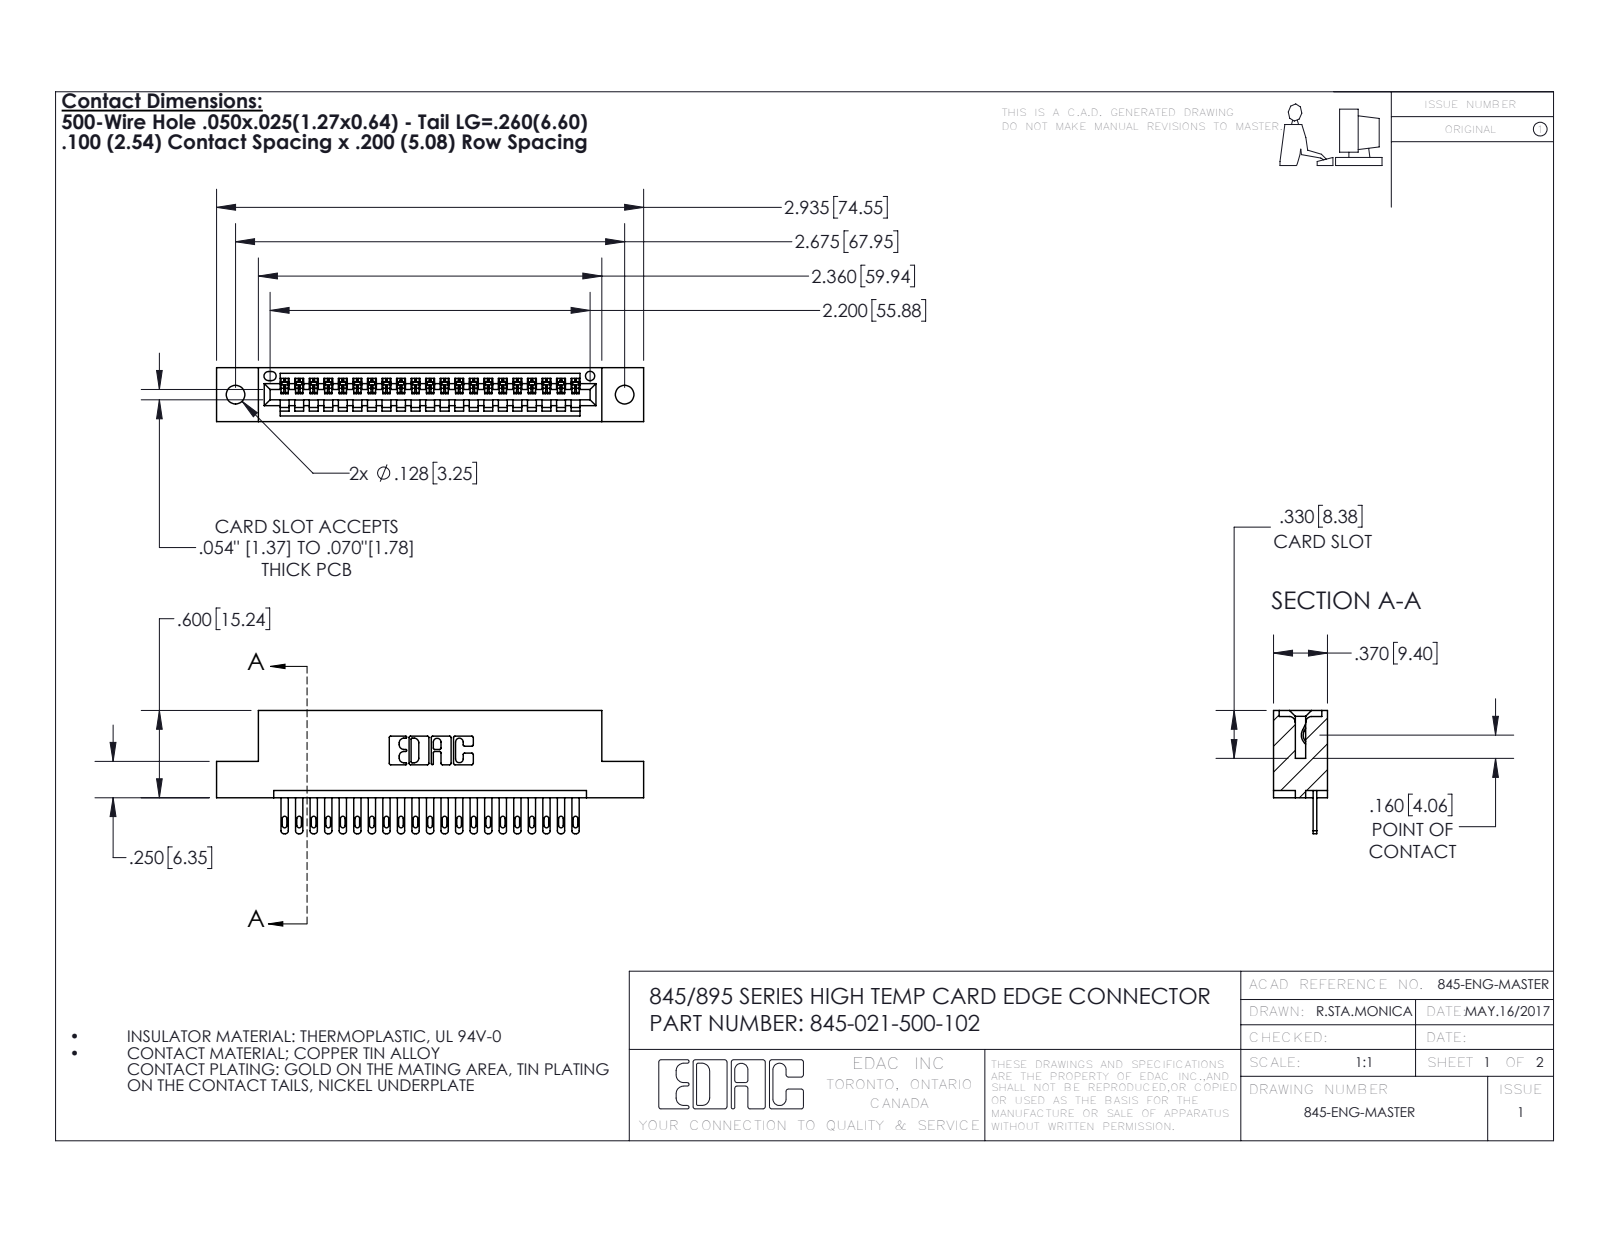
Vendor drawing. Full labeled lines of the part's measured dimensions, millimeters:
Part name (STEP PRODUCT): 345-292-001_345-293-100; 345 Part_Flush Mounting Lugs - 0.128 Dia; 345-021-500-102
STEP written by: SolidWorks 2016 (CONFIG_CONTROL_DESIGN)
Units: millimetres
Bodies: 22 solids, 1260 faces (794 planar, 466 cylindrical, 0 other)
Overall size (bounding box): 74.5 × 21.5 × 9.4
Volume: 6 880 mm³ · Surface area: 8 639 mm²
Round holes (diameter × count): ⌀3.3 ×2, ⌀1.6 ×1
Partial cylindrical surfaces — rounded edges, fillets, slot ends (radius × count): R0.2 ×42, R0.4 ×42, R0.5 ×42, R0.3 ×22, R0.2 ×6, R0.8 ×6, R0.7 ×3, R0.8 ×2
Main face-to-face distances: 7.6, 1.8, 5.1, 9.4, 2.5, 6.9, 0.6, 5.7, 3.8, 1.3
Hole centre spacings: 6.9, 62, 67.9
